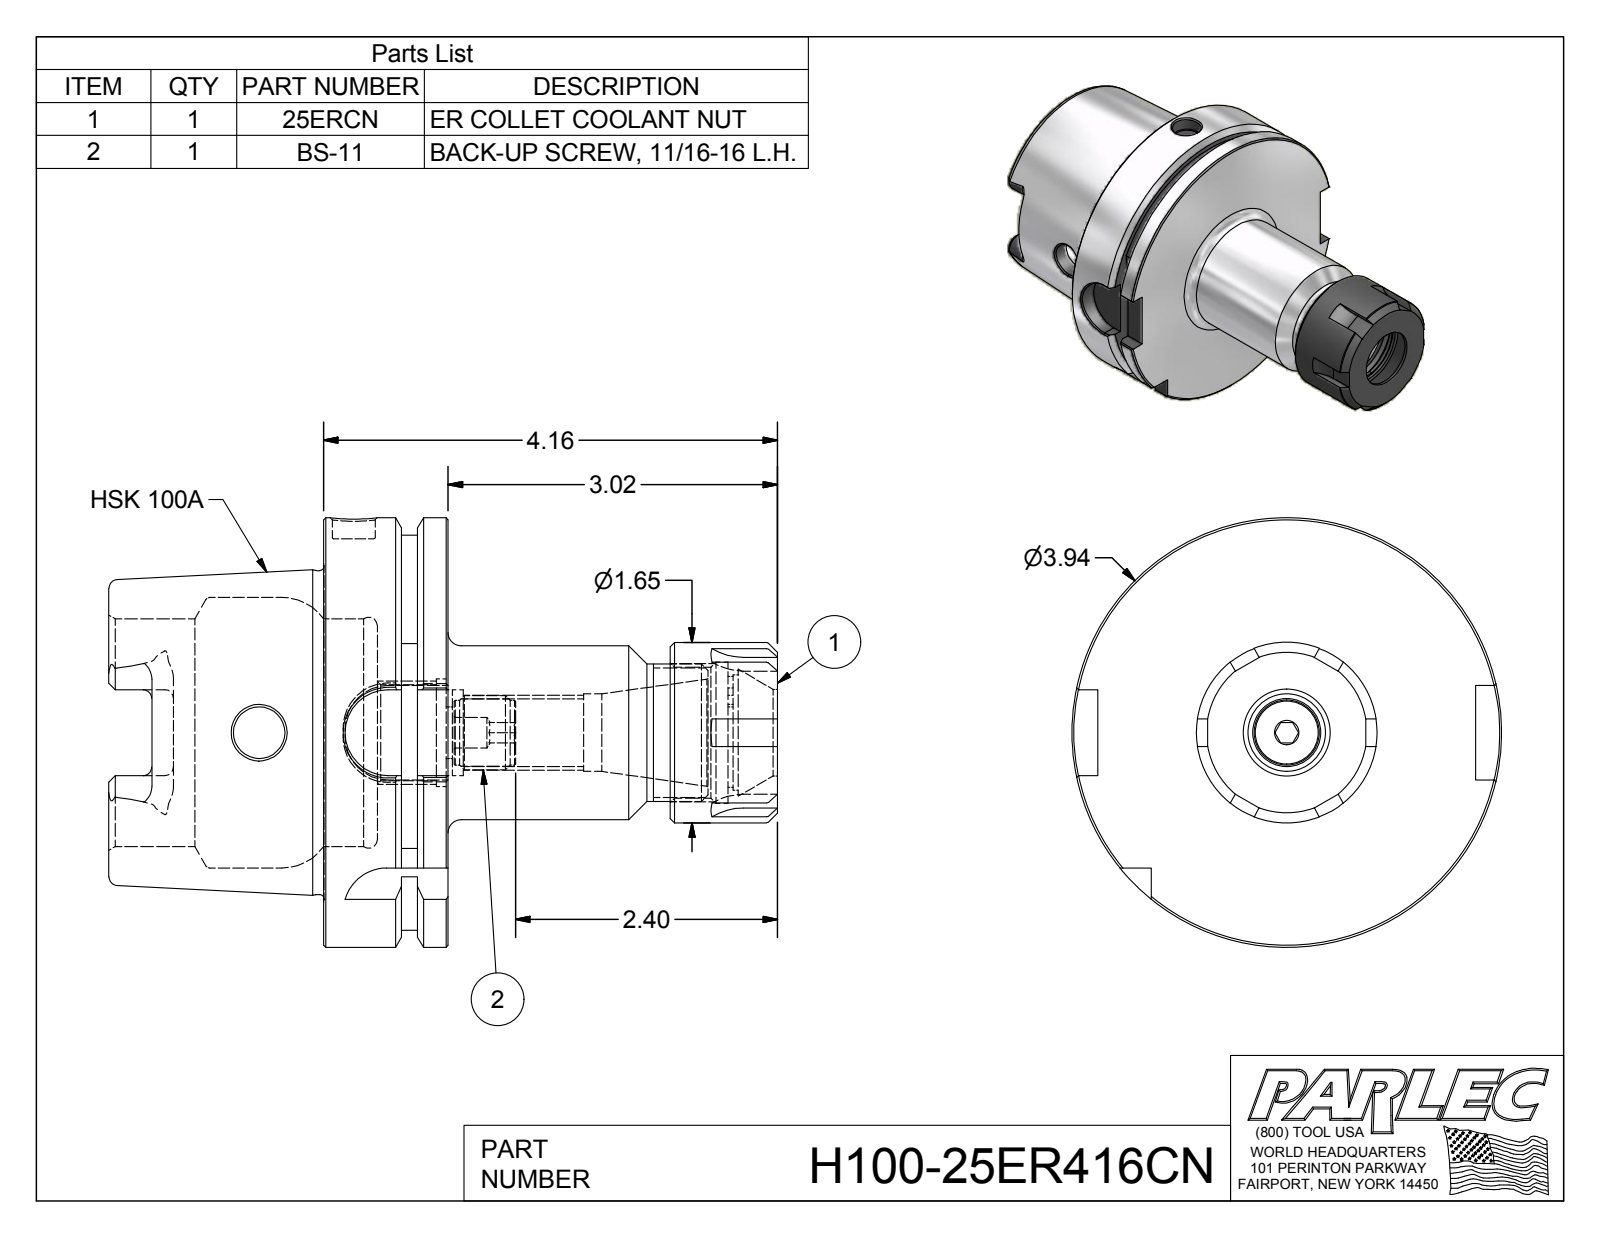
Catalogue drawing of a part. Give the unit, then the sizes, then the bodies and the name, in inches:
Units: inches
Overall size (bounding box): 6.129 × 3.937 × 3.937
Round holes (diameter × count): ⌀0.472 ×2, ⌀0.28 ×1, ⌀0.394 ×1, ⌀0.472 ×1, ⌀0.62 ×1, ⌀0.71 ×1, ⌀0.785 ×1, ⌀0.794 ×1, ⌀0.881 ×1, ⌀0.985 ×1, ⌀1.057 ×1, ⌀1.201 ×1
Round bosses / shafts (diameter × count): ⌀3.937 ×1, ⌀2.967 ×1, ⌀1.654 ×1, ⌀1.595 ×1, ⌀1.26 ×1, ⌀0.681 ×1, ⌀0.595 ×1
Partial cylindrical surfaces — rounded edges, fillets, slot ends (radius × count): R0.079 ×6, R0.5 ×6, R0.192 ×4, R0.394 ×4, R0.472 ×1, R0.515 ×1, R1.811 ×1
Main face-to-face distances: 1.142, 0.492, 0.65, 1.969, 2.461, 3.11, 6.128, 4.16, 3.668, 3.018
Volume: 19.97 in³ · Surface area: 107.4 in²
Bodies: 3 solids, 211 faces (82 planar, 57 cylindrical, 72 other)
Part name (STEP PRODUCT): H100-25ER416CN; H100-25ER4-1; 25ERCN; BS-11
STEP written by: Autodesk Inventor 2012 (AUTOMOTIVE_DESIGN)
